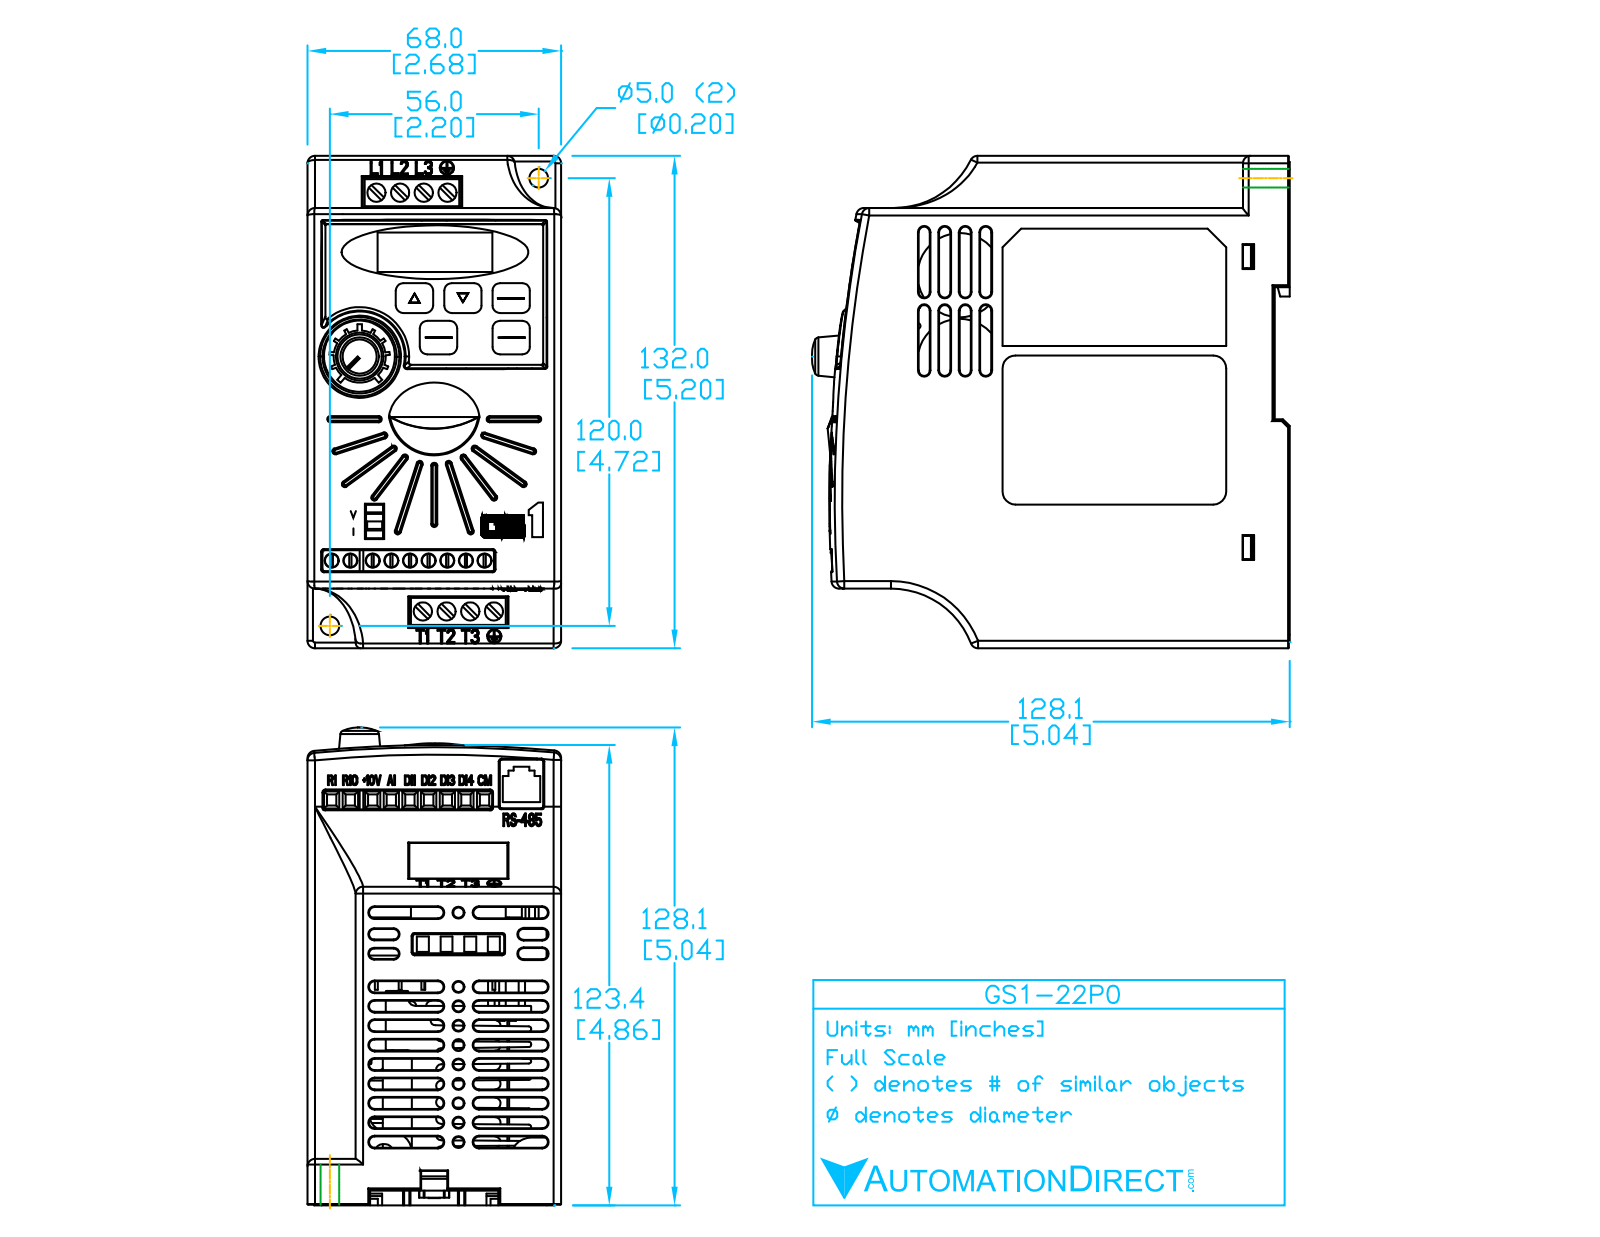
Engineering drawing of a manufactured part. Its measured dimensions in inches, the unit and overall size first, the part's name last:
Units: inches
Overall size (bounding box): 5.285 × 5.2 × 2.68
Round holes (diameter × count): ⌀0.15 ×9, ⌀0.187 ×8, ⌀0.2 ×2
Round bosses / shafts (diameter × count): ⌀0.316 ×5
Partial cylindrical surfaces — rounded edges, fillets, slot ends (radius × count): R0.03 ×38, R0.1 ×22, R0.06 ×20, R0.063 ×6, R0.015 ×2, R0.093 ×2, R0.2 ×2, R0.44 ×2
Main face-to-face distances: 2.68, 0.175, 5.2, 0.015, 5.185, 0.167, 0.55, 4.65, 0.535, 0.62
Hole centre spacings: 0.2, 0.4, 0.6, 0.8, 1, 1.2, 1.4, 3.921
Volume: 61.51 in³ · Surface area: 109.5 in²
Bodies: 1 solid, 891 faces (536 planar, 168 cylindrical, 187 other)
Part name (STEP PRODUCT): GS1-22P0
STEP written by: SolidWorks 2015 (AUTOMOTIVE_DESIGN)
